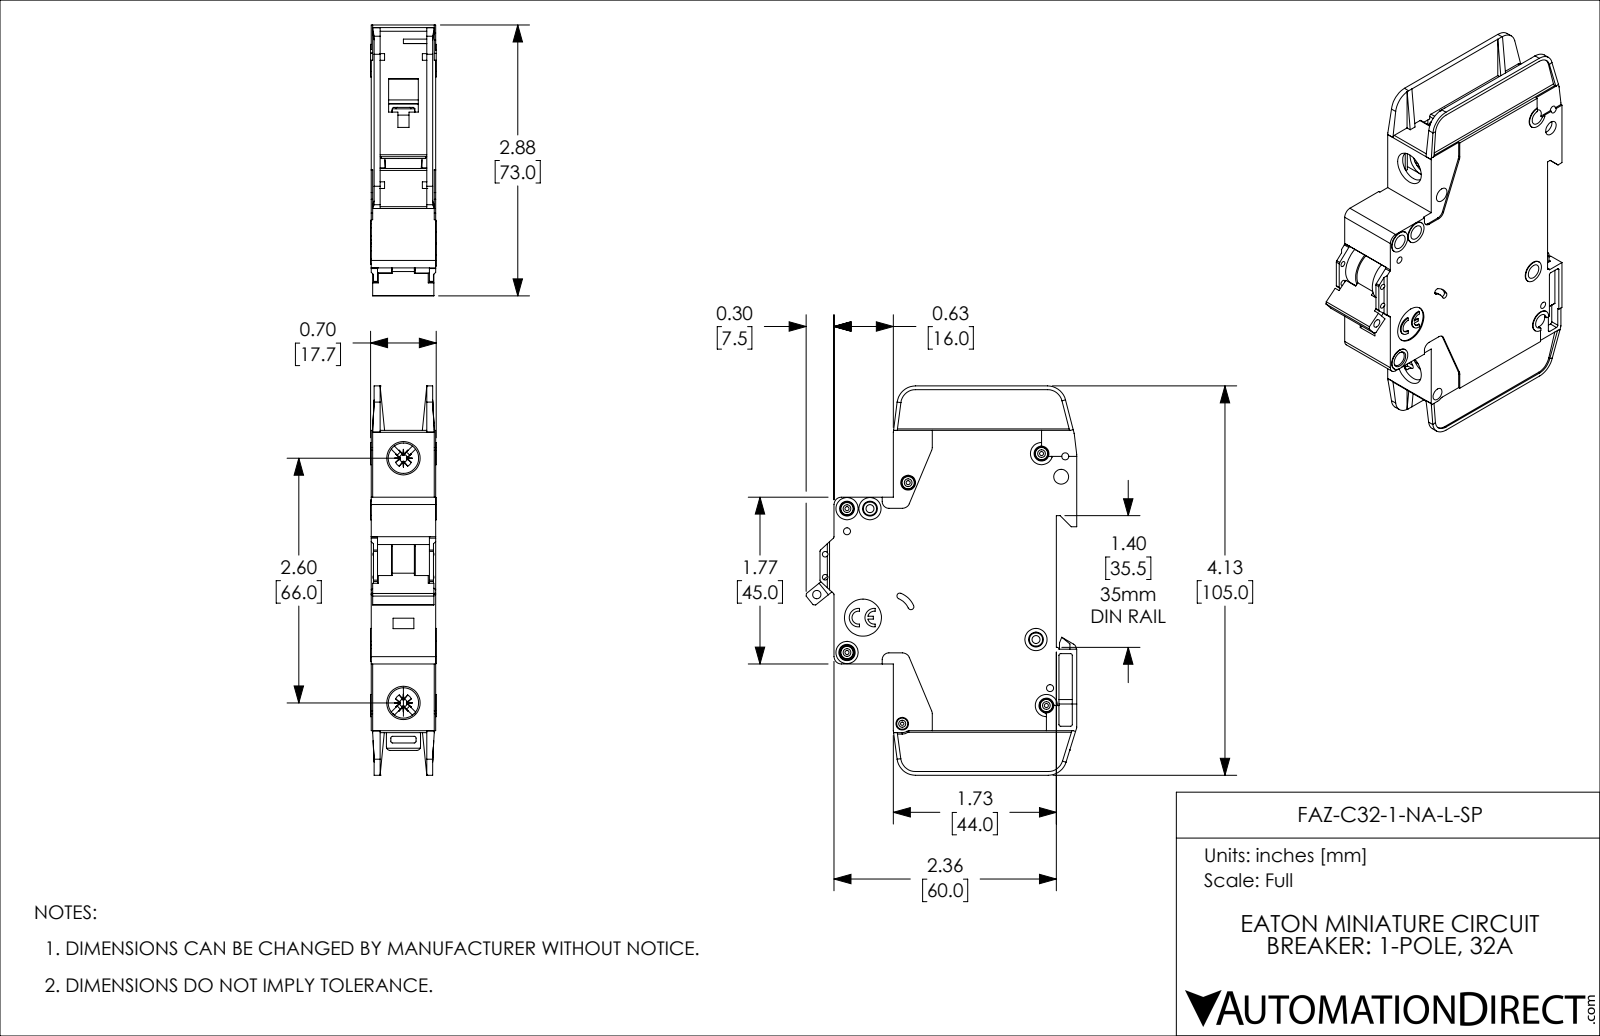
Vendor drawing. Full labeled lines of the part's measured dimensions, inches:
Part name (STEP PRODUCT): FAZ-C32-1-NA-L-SP
STEP written by: SolidWorks 2019 (AUTOMOTIVE_DESIGN)
Units: inches
Bodies: 1 solid, 1127 faces (671 planar, 357 cylindrical, 99 other)
Overall size (bounding box): 4.134 × 2.876 × 0.697
Volume: 4.682 in³ · Surface area: 41.01 in²
Round holes (diameter × count): ⌀0.157 ×8, ⌀0.043 ×5, ⌀0.075 ×4, ⌀0.059 ×2, ⌀0.085 ×2, ⌀0.323 ×2, ⌀0.035 ×1, ⌀0.089 ×1, ⌀0.098 ×1, ⌀0.134 ×1, ⌀0.394 ×1
Round bosses / shafts (diameter × count): ⌀0.13 ×5, ⌀0.236 ×4, ⌀0.118 ×2, ⌀0.098 ×1
Partial cylindrical surfaces — rounded edges, fillets, slot ends (radius × count): R0.02 ×42, R0.016 ×10, R0.039 ×10, R0.079 ×8, R0.197 ×5, R0.008 ×4, R0.026 ×4, R0.043 ×4
Main face-to-face distances: 0.047, 0.685, 0.591, 0.638, 0.094, 0.543, 0.016, 0.031, 0.496, 0.575
Hole centre spacings: 0.244, 0.537, 0.87, 0.189, 0.199, 0.204, 0.221, 0.24
